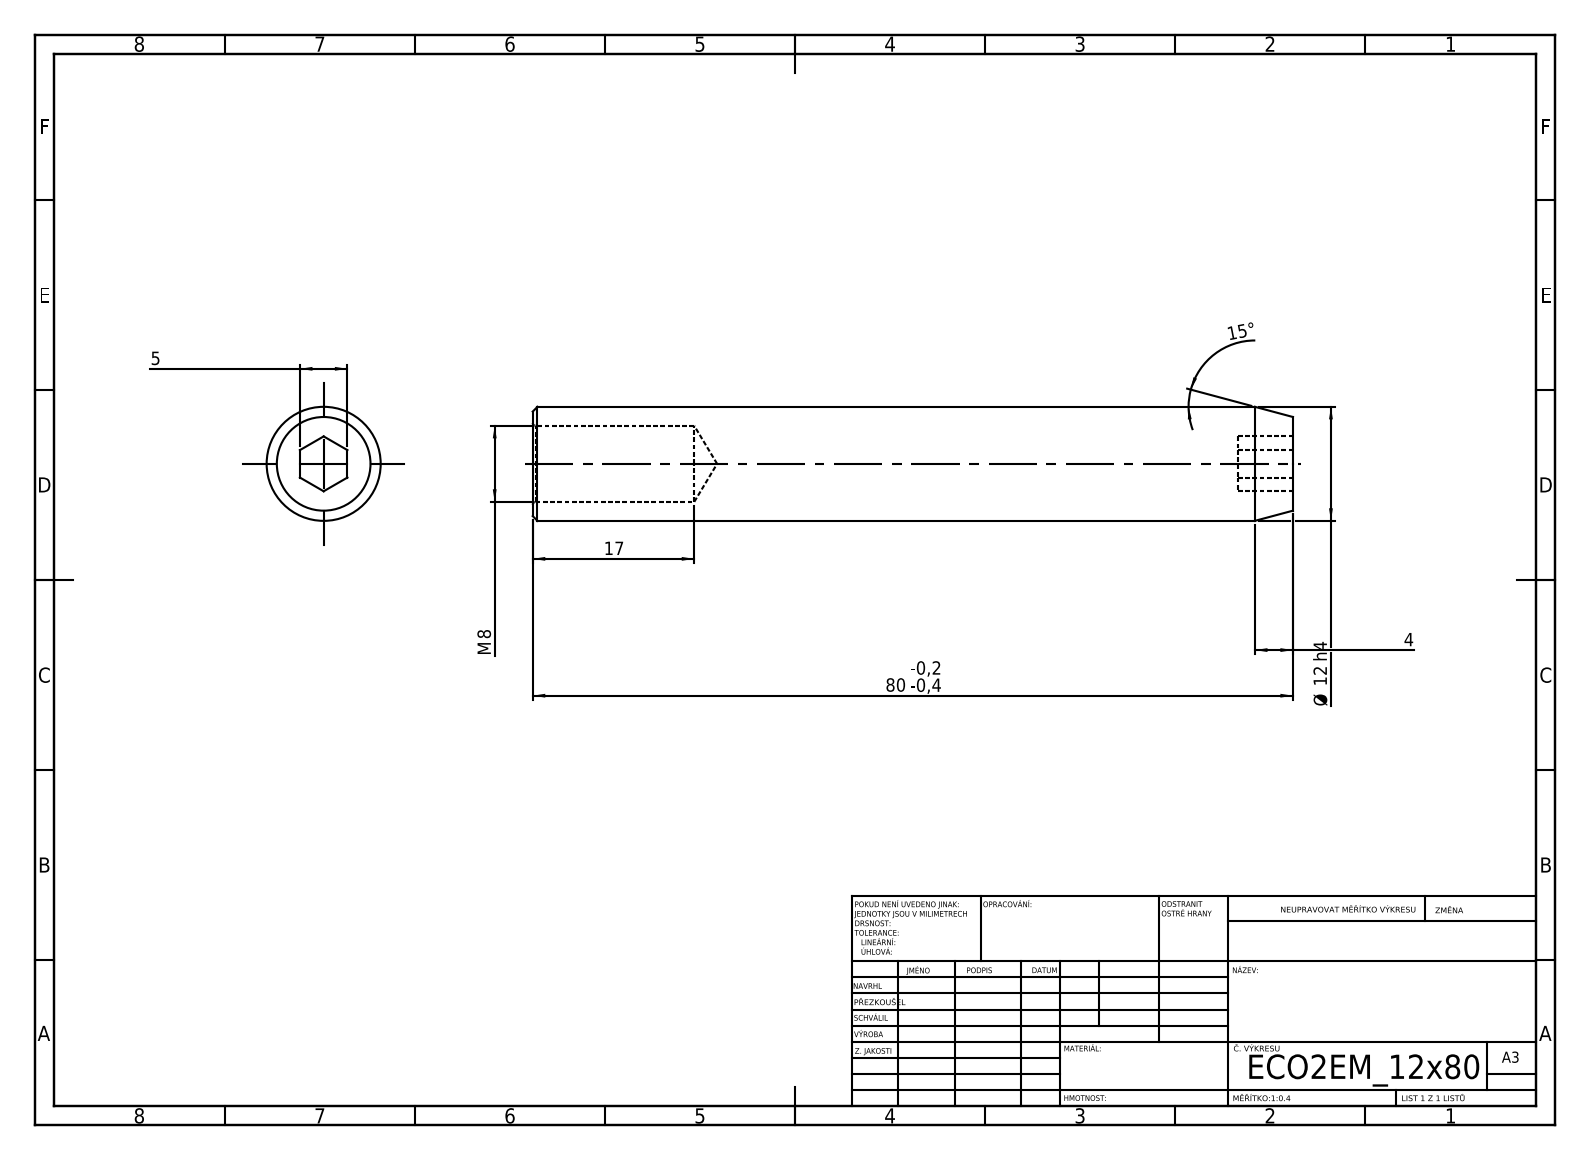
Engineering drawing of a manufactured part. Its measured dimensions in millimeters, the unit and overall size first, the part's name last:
Units: millimetres
Overall size (bounding box): 80 × 12 × 12
Round holes (diameter × count): ⌀8 ×1
Round bosses / shafts (diameter × count): ⌀12 ×1
Main face-to-face distances: 5, 80, 5.8, 74.2
Volume: 7 946 mm³ · Surface area: 3 718 mm²
Bodies: 1 solid, 21 faces (9 planar, 4 cylindrical, 8 other)
STEP written by: SolidWorks 2019 (CONFIG_CONTROL_DESIGN)
